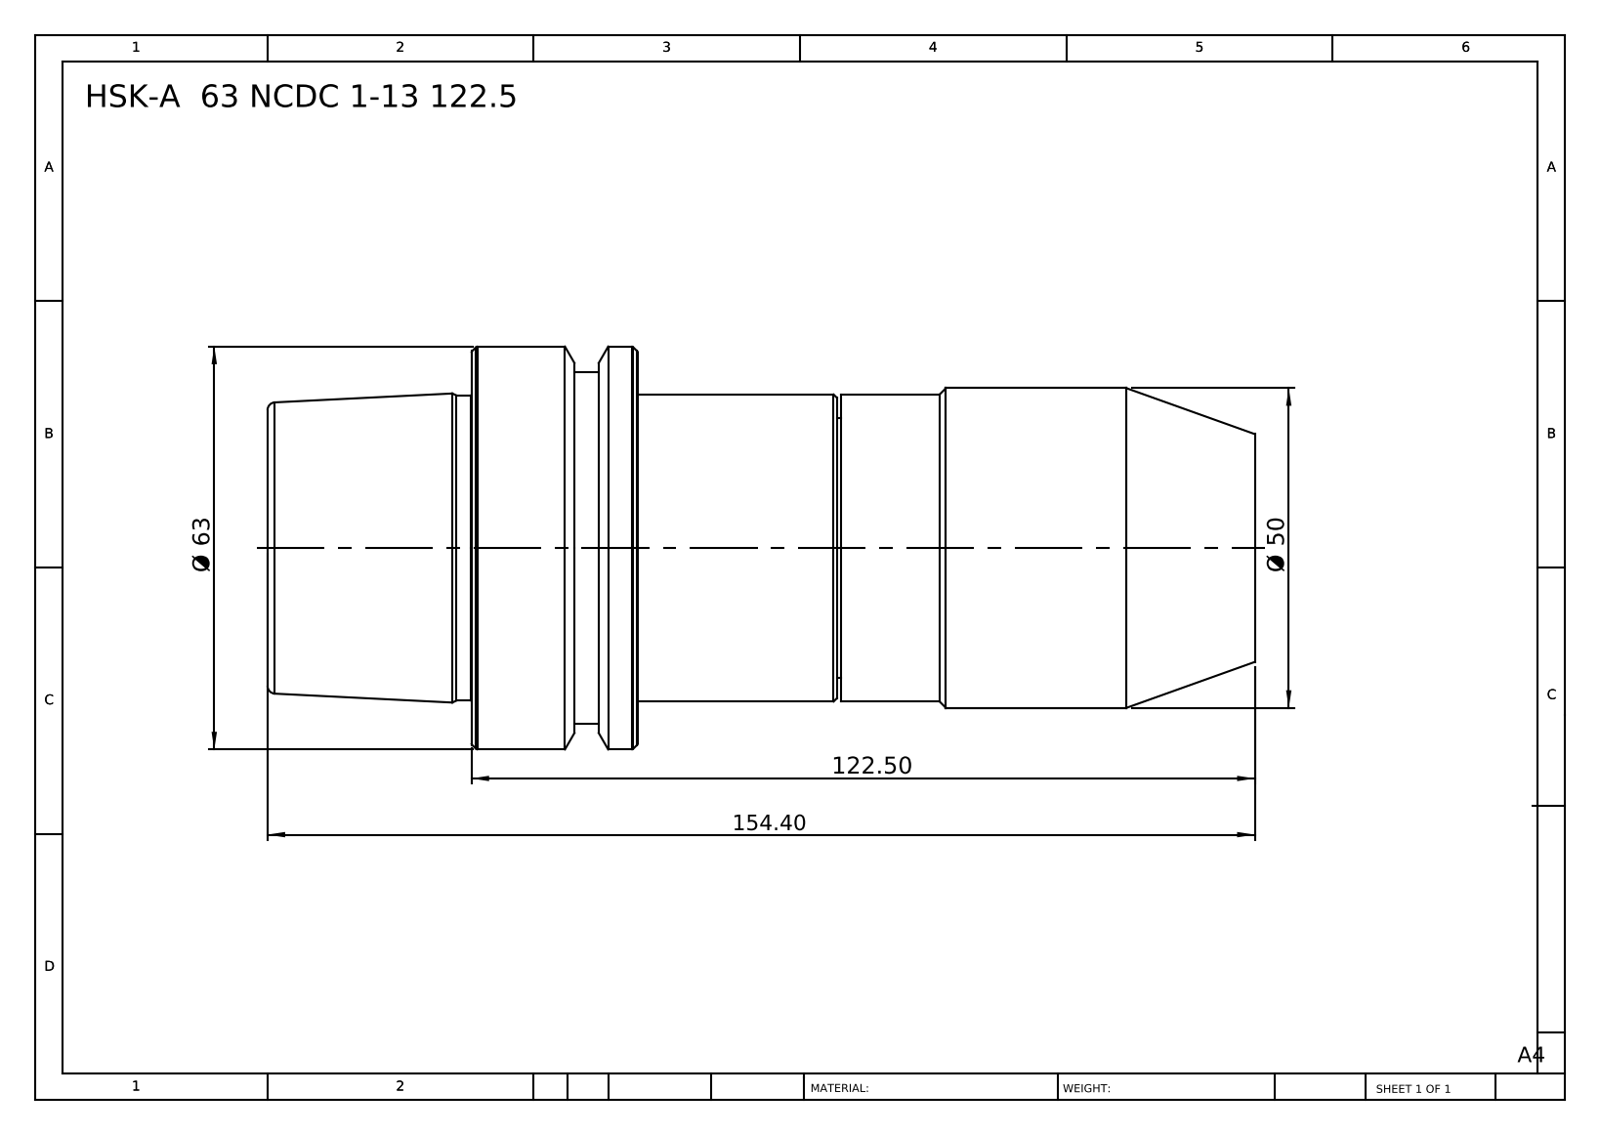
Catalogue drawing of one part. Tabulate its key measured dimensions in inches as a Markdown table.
| quantity | value |
| --- | --- |
| part name | HSK-A 63 NCDC 1-13 122.5 |
| STEP written by | SolidWorks 2014 (CONFIG_CONTROL_DESIGN) |
| units | inches |
| bodies | 1 solid, 56 faces (8 planar, 16 cylindrical, 32 other) |
| overall size | 6.079 × 2.48 × 2.48 |
| volume | 18.56 in³ |
| surface area | 48.71 in² |
| round bosses / shafts (diameter × count) | 2.48 × 1, 2.165 × 1, 1.969 × 1, 1.89 × 1, 1.881 × 1, 1.604 × 1 |
| main face-to-face distances | 2.28, 3.799, 6.079, 4.823, 1.024, 1.256, 2.547, 1.252, 2.276, 3.531 |
